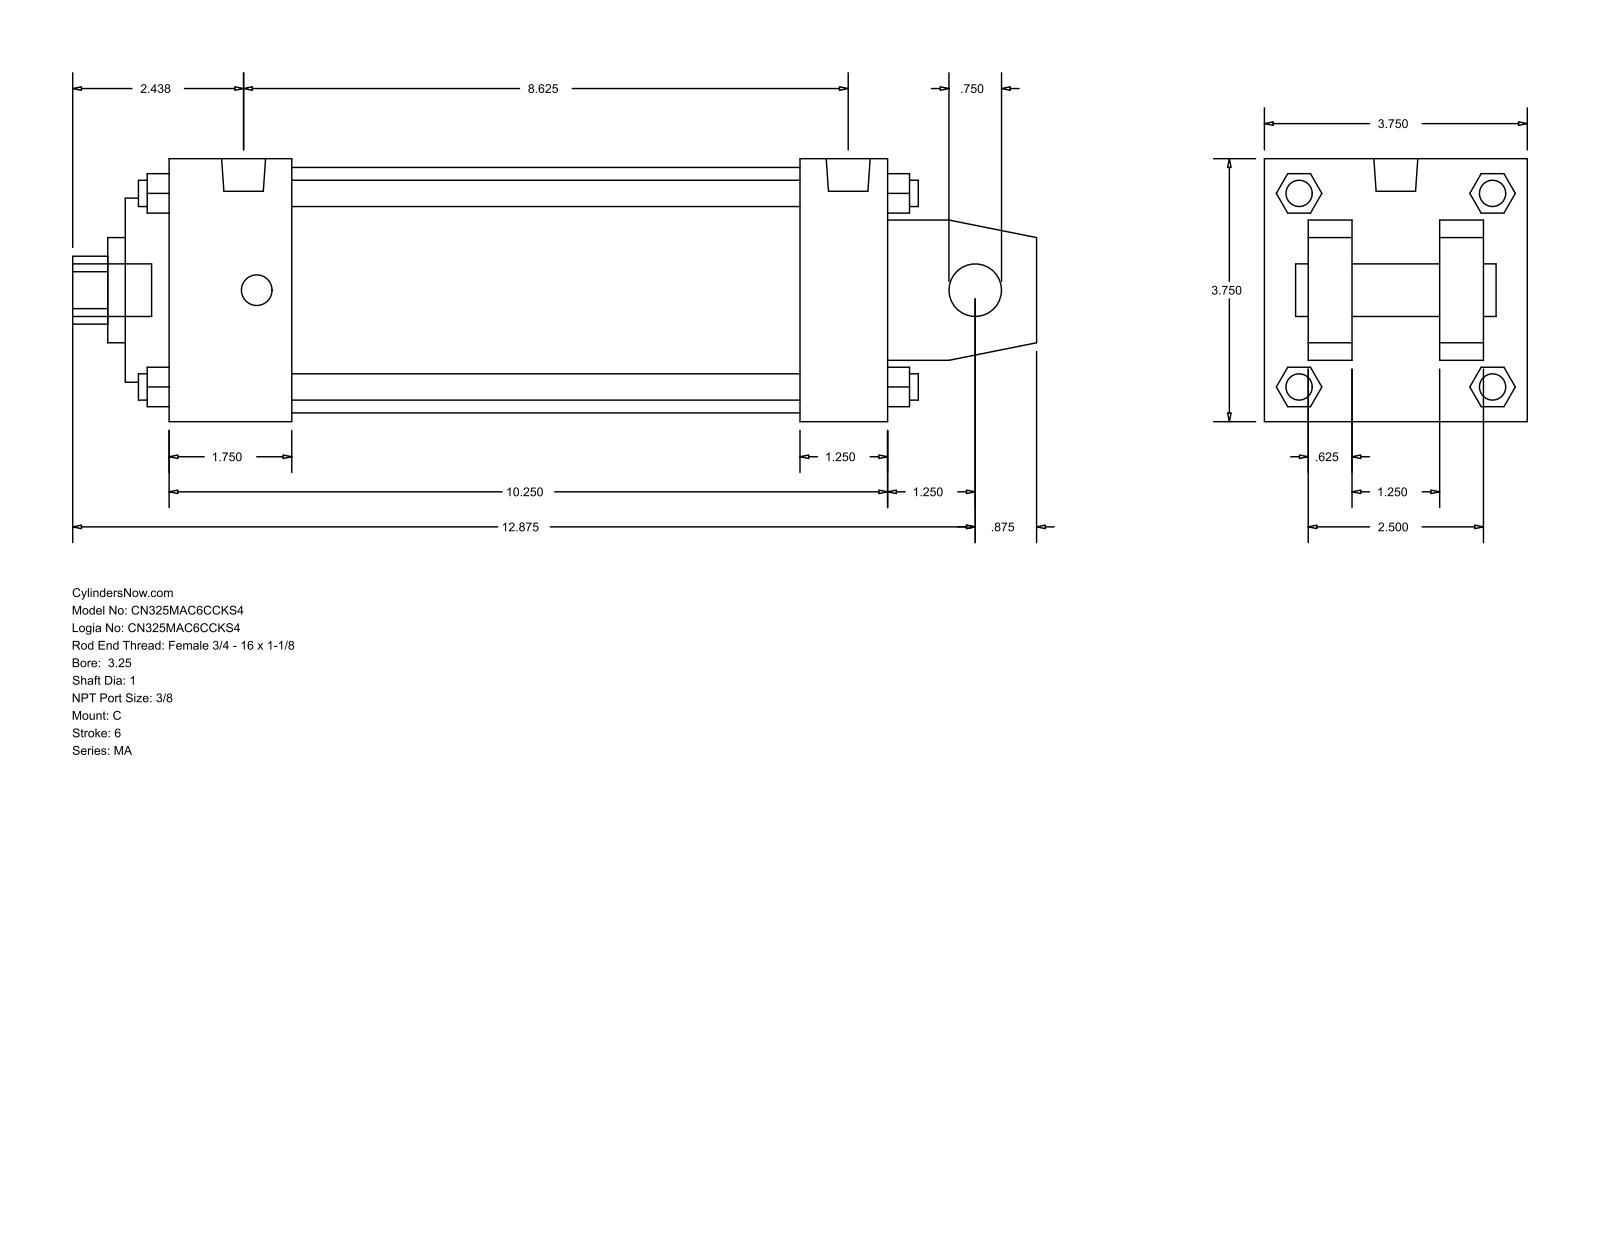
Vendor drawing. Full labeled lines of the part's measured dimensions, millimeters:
Part name (STEP PRODUCT): MA_C__0325_1
STEP written by: GSSL Pune (CONFIG_CONTROL_DESIGN)
Units: millimetres
Bodies: 0 solids, 141 faces (109 planar, 32 cylindrical, 0 other)
Overall size (bounding box): 349.25 × 95.25 × 95.25
Round holes (diameter × count): ⌀19.05 ×1, ⌀25.4 ×1, ⌀38.1 ×1, ⌀66.67 ×1, ⌀88.9 ×1
Round bosses / shafts (diameter × count): ⌀11.11 ×4, ⌀9.53 ×4, ⌀15.93 ×2, ⌀19.05 ×1
Partial cylindrical surfaces — rounded edges, fillets, slot ends (radius × count): R12.29 ×1
Main face-to-face distances: 95.24, 15.87, 63.5, 260.35, 31.74, 79.37, 47.63, 276.22, 228.6, 31.75
